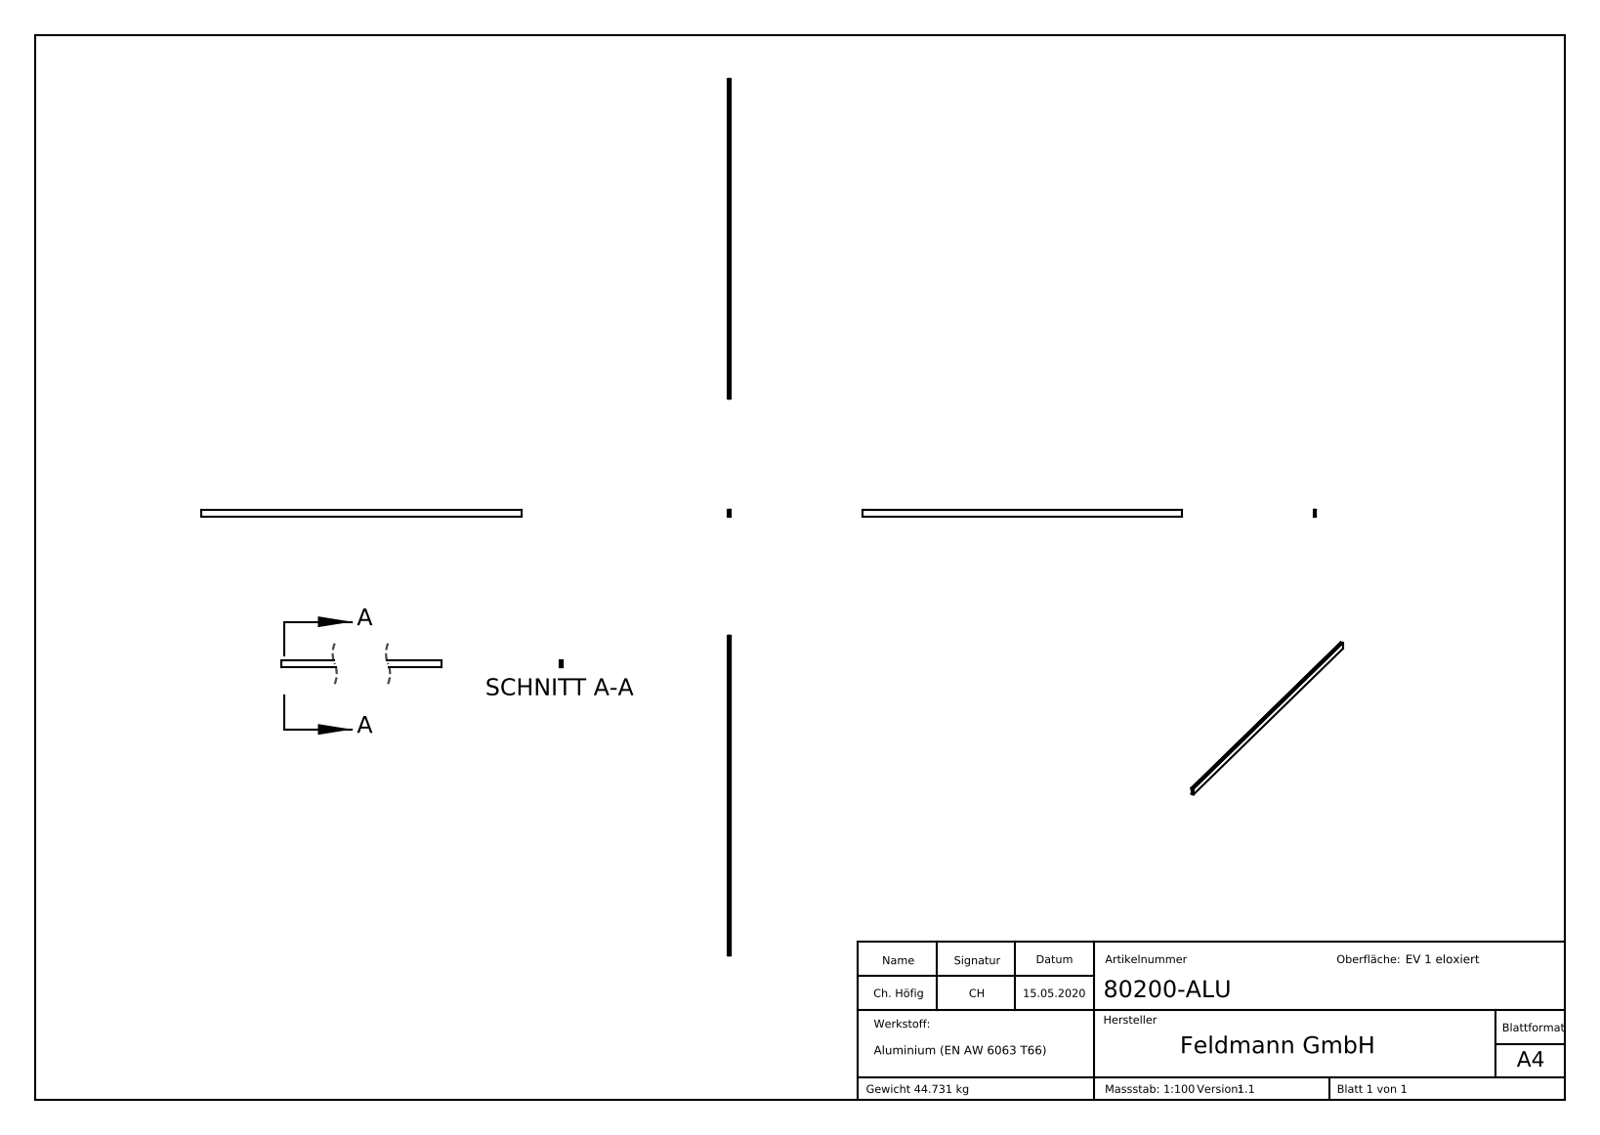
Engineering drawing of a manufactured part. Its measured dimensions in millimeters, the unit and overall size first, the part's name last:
Units: millimetres
Overall size (bounding box): 6000 × 125 × 47
Round holes (diameter × count): ⌀13 ×60
Partial cylindrical surfaces — rounded edges, fillets, slot ends (radius × count): R11.2 ×60, R0.5 ×4, R1 ×3, R0.65 ×2, R0.25 ×1
Main face-to-face distances: 47, 12, 35, 7.94, 39.06, 4.06, 27.06, 23, 3, 15
Hole centre spacings: 100, 200, 300, 400, 500, 600, 700, 800
Volume: 16 570 000 mm³ · Surface area: 3 373 000 mm²
Bodies: 1 solid, 667 faces (191 planar, 251 cylindrical, 225 other)
Part name (STEP PRODUCT): 80200-ALU
STEP written by: SolidWorks 2015 (CONFIG_CONTROL_DESIGN)
